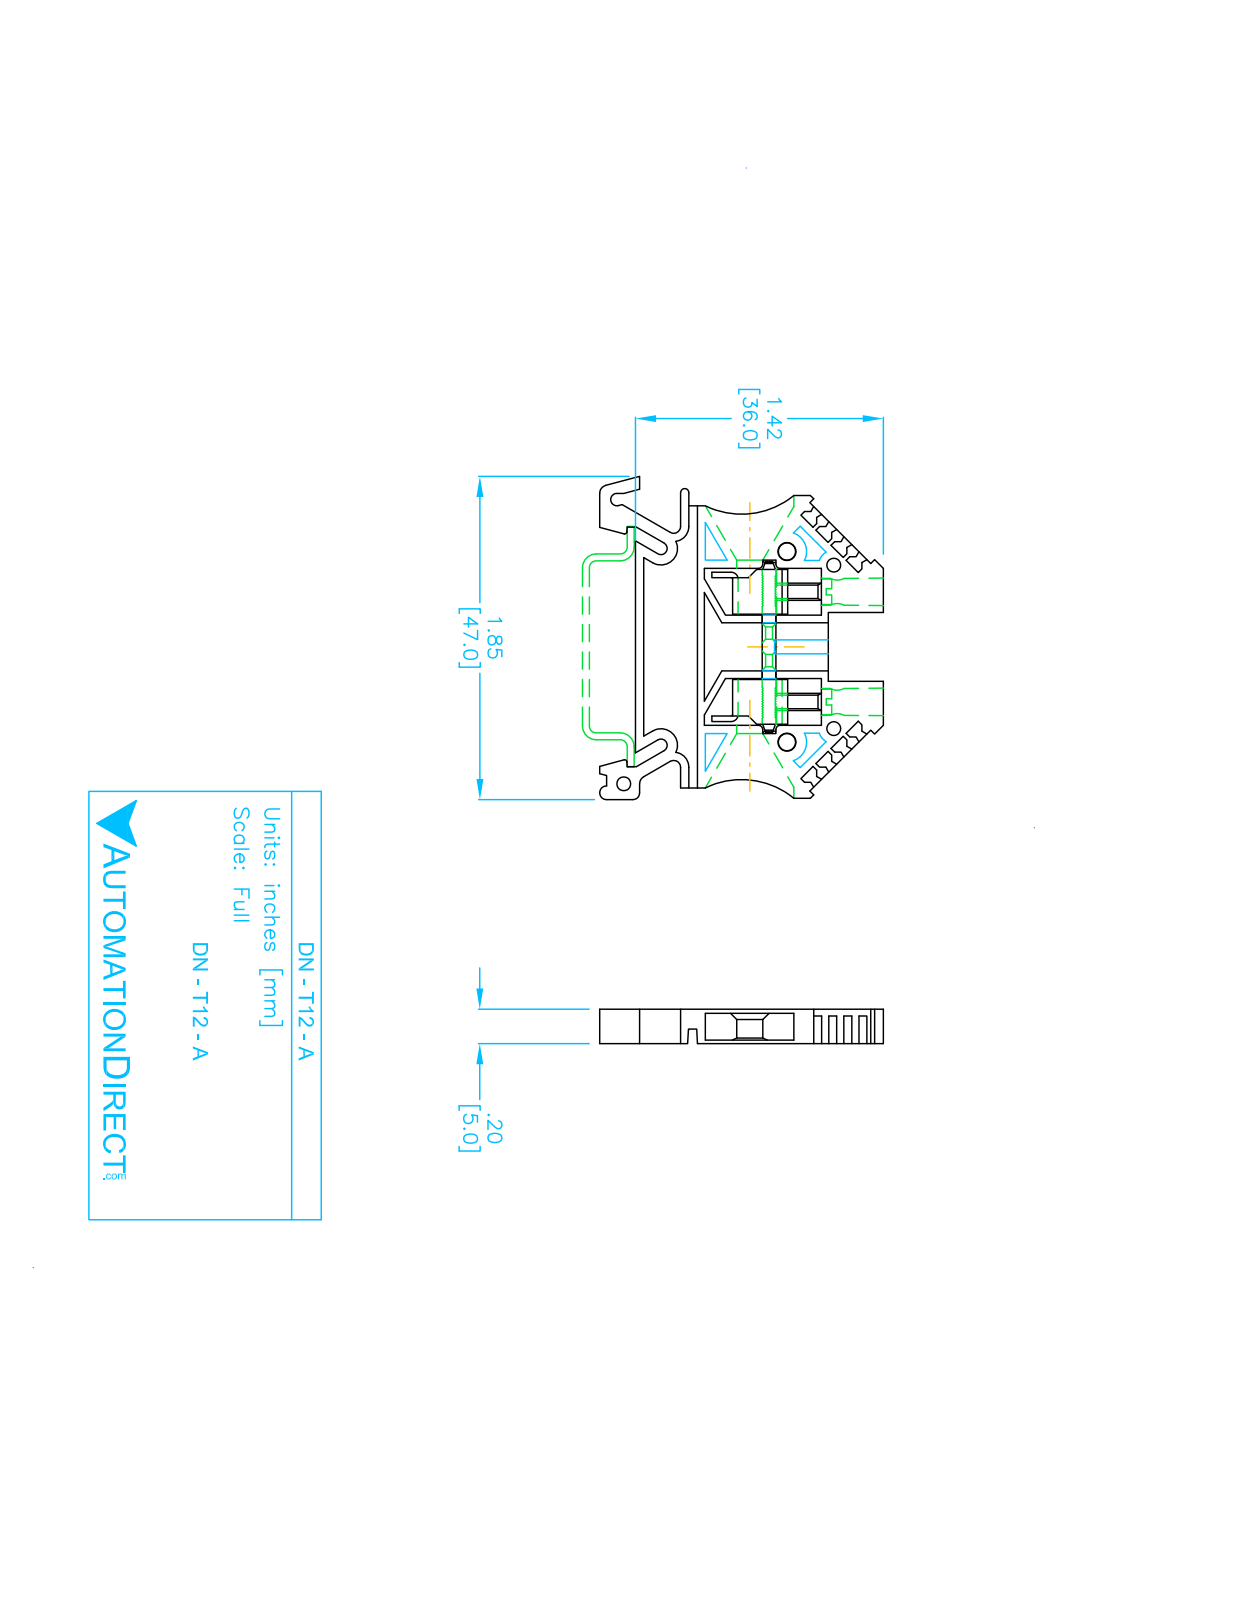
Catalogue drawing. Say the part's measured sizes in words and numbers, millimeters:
The part is named "43408_DN-T12-A". Its 3-D file was written by "SolidWorks 2013 (AUTOMOTIVE_DESIGN)". It is 1 solid with 169 faces: 134 planar, 35 cylindrical and 0 other. Overall it measures 46.98 by 41.2 by 5 millimeters. Its volume is 5 010 cubic millimeters and its surface area 4 601 square millimeters. Round holes: 2 of diameter 4.17, 1 of diameter 2. Partial cylindrical surfaces (rounded edges, fillets, slot ends): 4 of radius 1, 3 of radius 0.9, 2 of radius 0.3, 2 of radius 1.2, 2 of radius 2.2, 2 of radius 2.4, 2 of radius 12, 1 of radius 0.6. The main face-to-face distances are 4.8, 5, 2.2, 0.5, 2.7, 2.4, 2.9, 2.1, 2.6, 9. The hole center spacings are 14.96.
